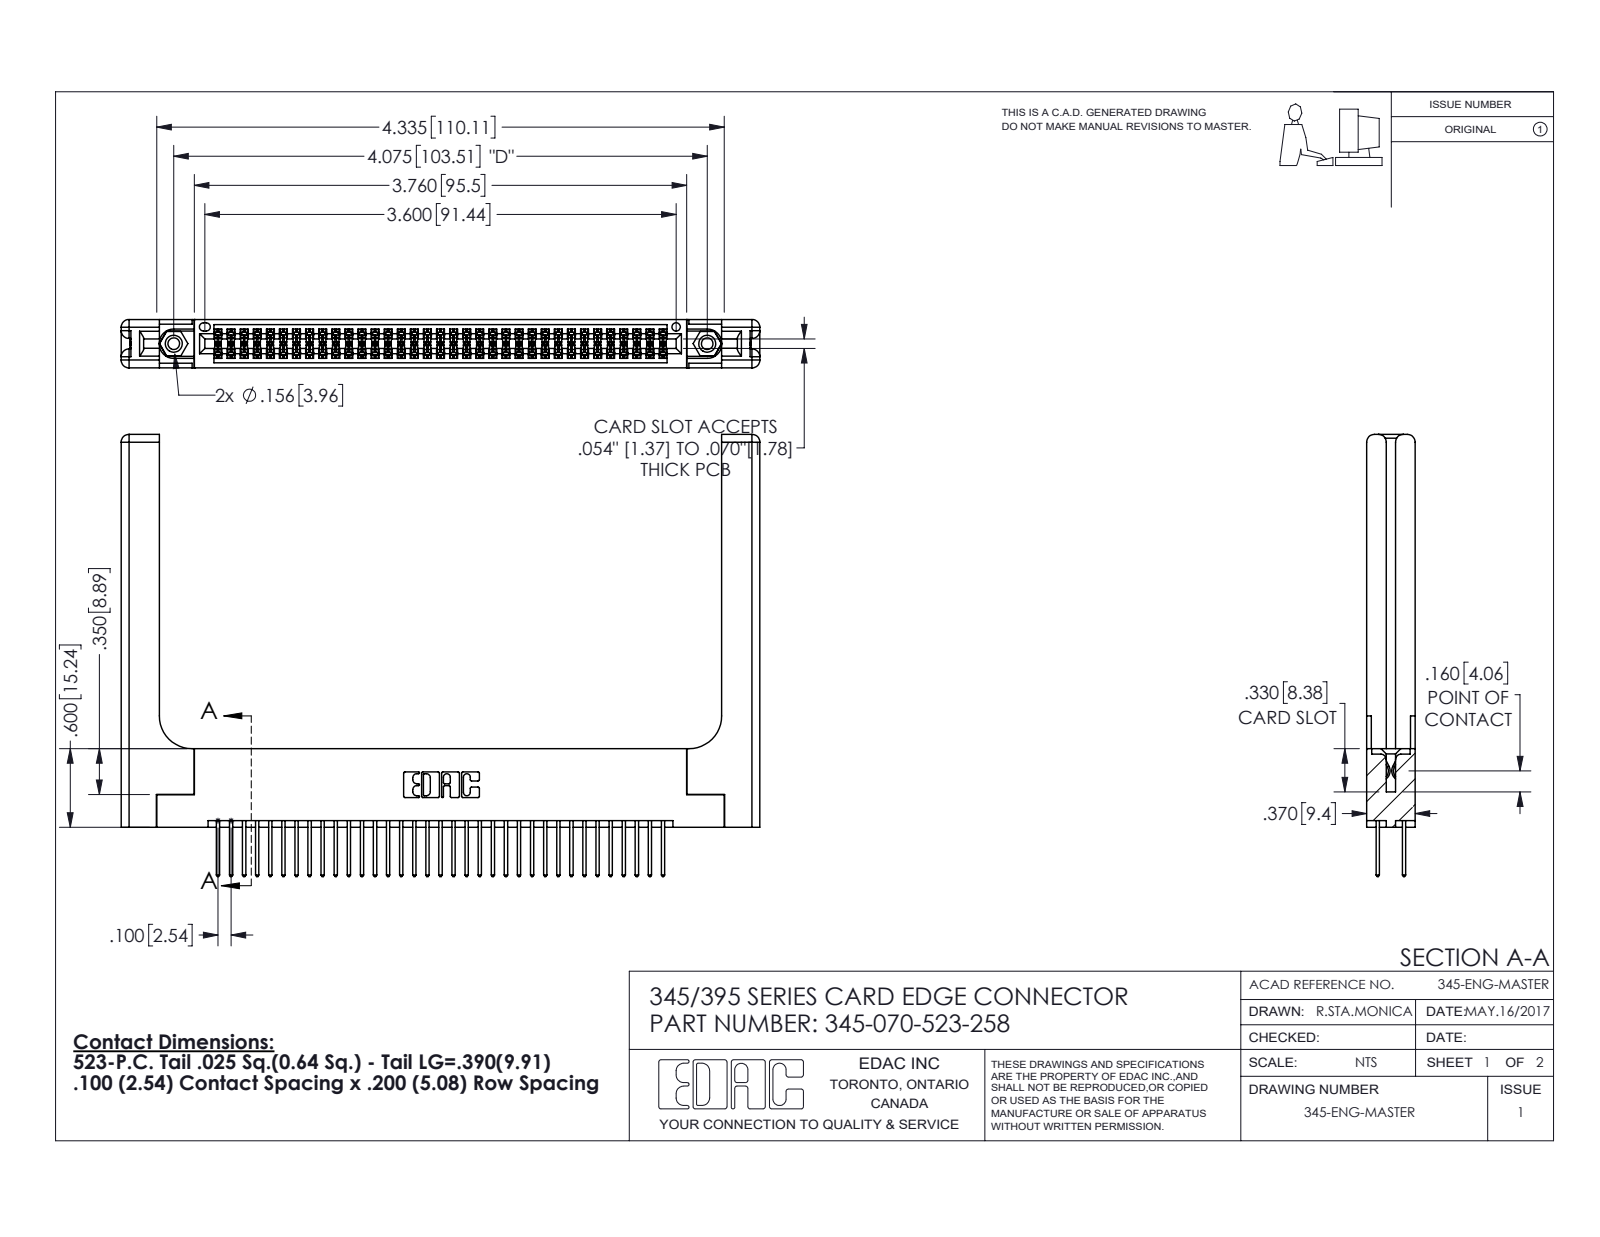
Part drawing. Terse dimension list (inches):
name: 345-070-523-258; 345-292-001_345-293-123; 345 Part_Flush Mounting Lugs - 0.156 Dia-TH; 345-250-001_345-250-001-102 (+1 more)
written by: SolidWorks 2016 (CONFIG_CONTROL_DESIGN)
unit: in
bodies: 75 solids, 3882 faces (2538 planar, 1284 cylindrical, 60 other)
size: 4.879 × 3.377 × 0.37
volume: 1.257 in³; area: 36.39 in²
holes: 2× ⌀0.089, 2× ⌀0.125, 2× ⌀0.156, 1× ⌀0.064
bosses: 2× ⌀0.155
rounds: 105× R0.006, 70× R0.01, 22× R0.01, 16× R0.06, 6× R0.007, 6× R0.031, 3× R0.026, 2× R0.014
face distances: 0.072, 0.298, 0.37, 0.2, 0.098, 0.272, 0.025, 0.225, 0.148, 0.15
hole spacings: 0.27, 3.839, 4.075
